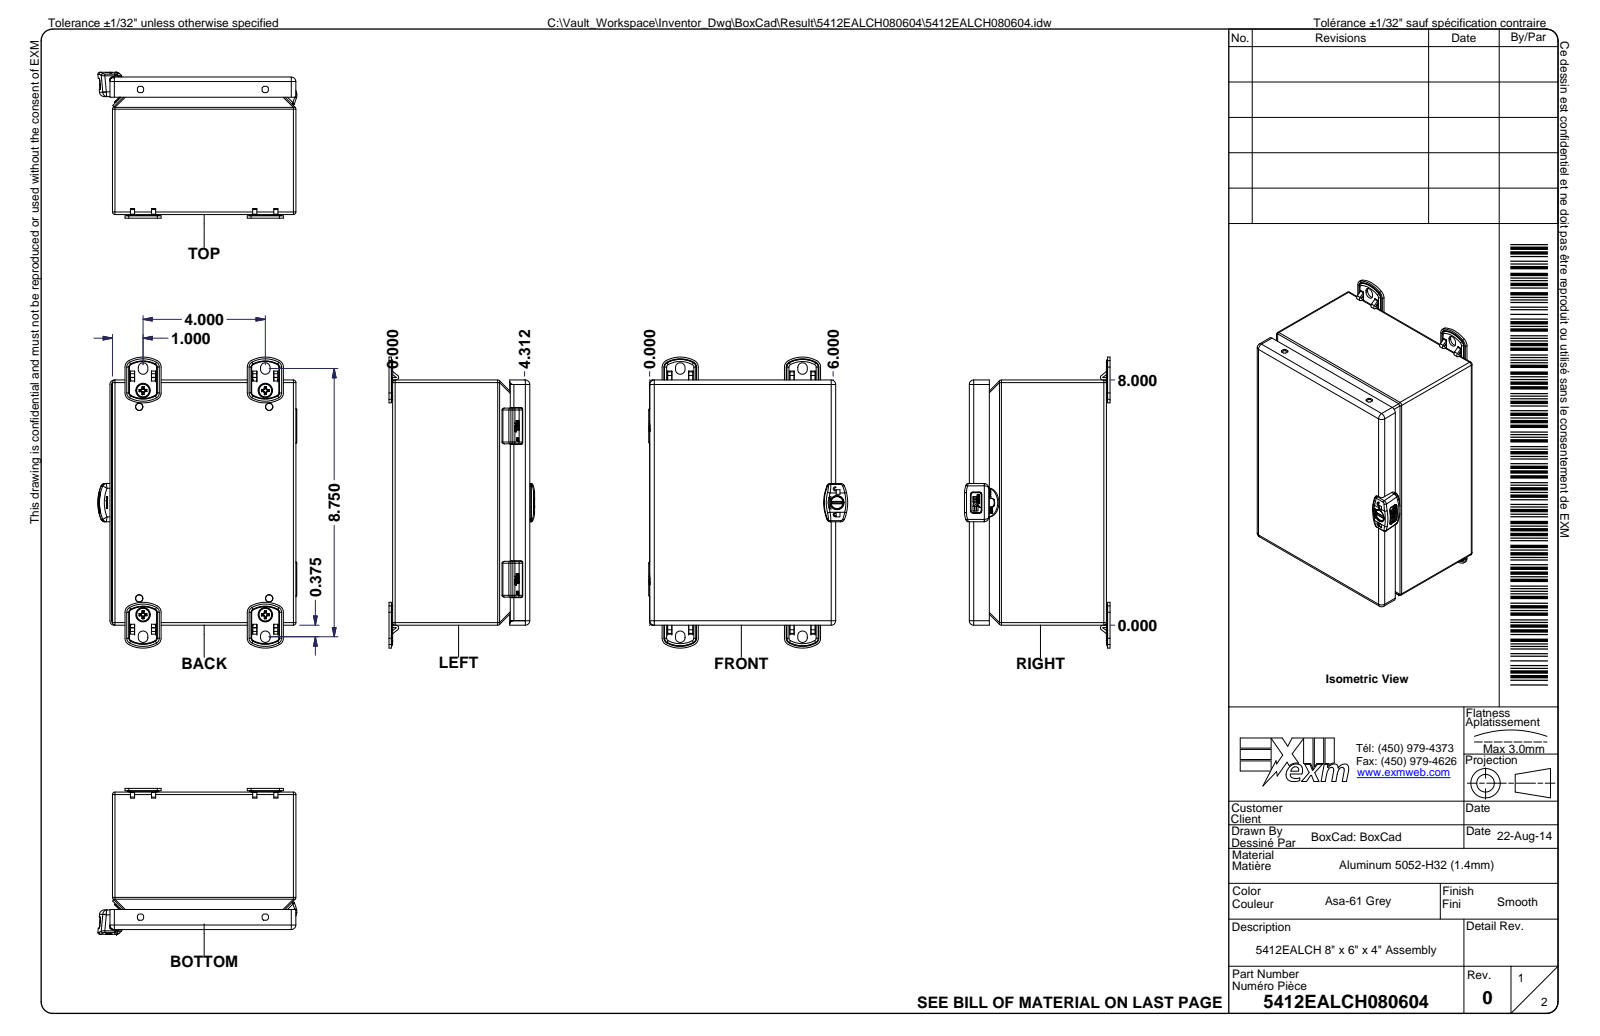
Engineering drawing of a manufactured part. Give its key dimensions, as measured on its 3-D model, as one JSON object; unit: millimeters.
{"part_name": "5412EALCH080604; 5412EALCH080604B; 5412EALCH080604B-P; STK-A-70469-1 (+8 more)", "step_written_by": "Autodesk Inventor 2020 (AUTOMOTIVE_DESIGN)", "units": "millimeters", "bodies": {"solids": 51, "faces": 6818, "planar": 2990, "cylindrical": 1592, "other": 2236}, "overall_size": [241.2, 165.2, 120.9], "volume_mm3": 295600, "surface_area_mm2": 415500, "round_holes": [[5, 6], [5, 4], [6, 4], [8.1, 4], [4.2, 3], [4.4, 3], [6, 3], [0.8, 2], [4.4, 2], [5.1, 2], [6.1, 2], [10, 2]], "round_bosses_or_shafts": [[5.9, 8], [12.7, 4], [6, 4], [7.6, 3], [5, 3], [4.9, 3], [10, 2], [0.9, 2]], "partial_cylinders_radius": [[0.5, 213], [0.3, 152], [1, 78], [0.2, 60], [1.5, 55], [0.1, 54], [0.8, 33], [2.1, 24]], "face_to_face_distances": [1.3, 1.3, 151.1, 112.6, 111.3, 201.9, 113.9, 112.6, 6, 7.7], "hole_center_spacings": [105.6, 13.8, 108, 158.8, 172.3, 192, 201.6, 155.2]}
